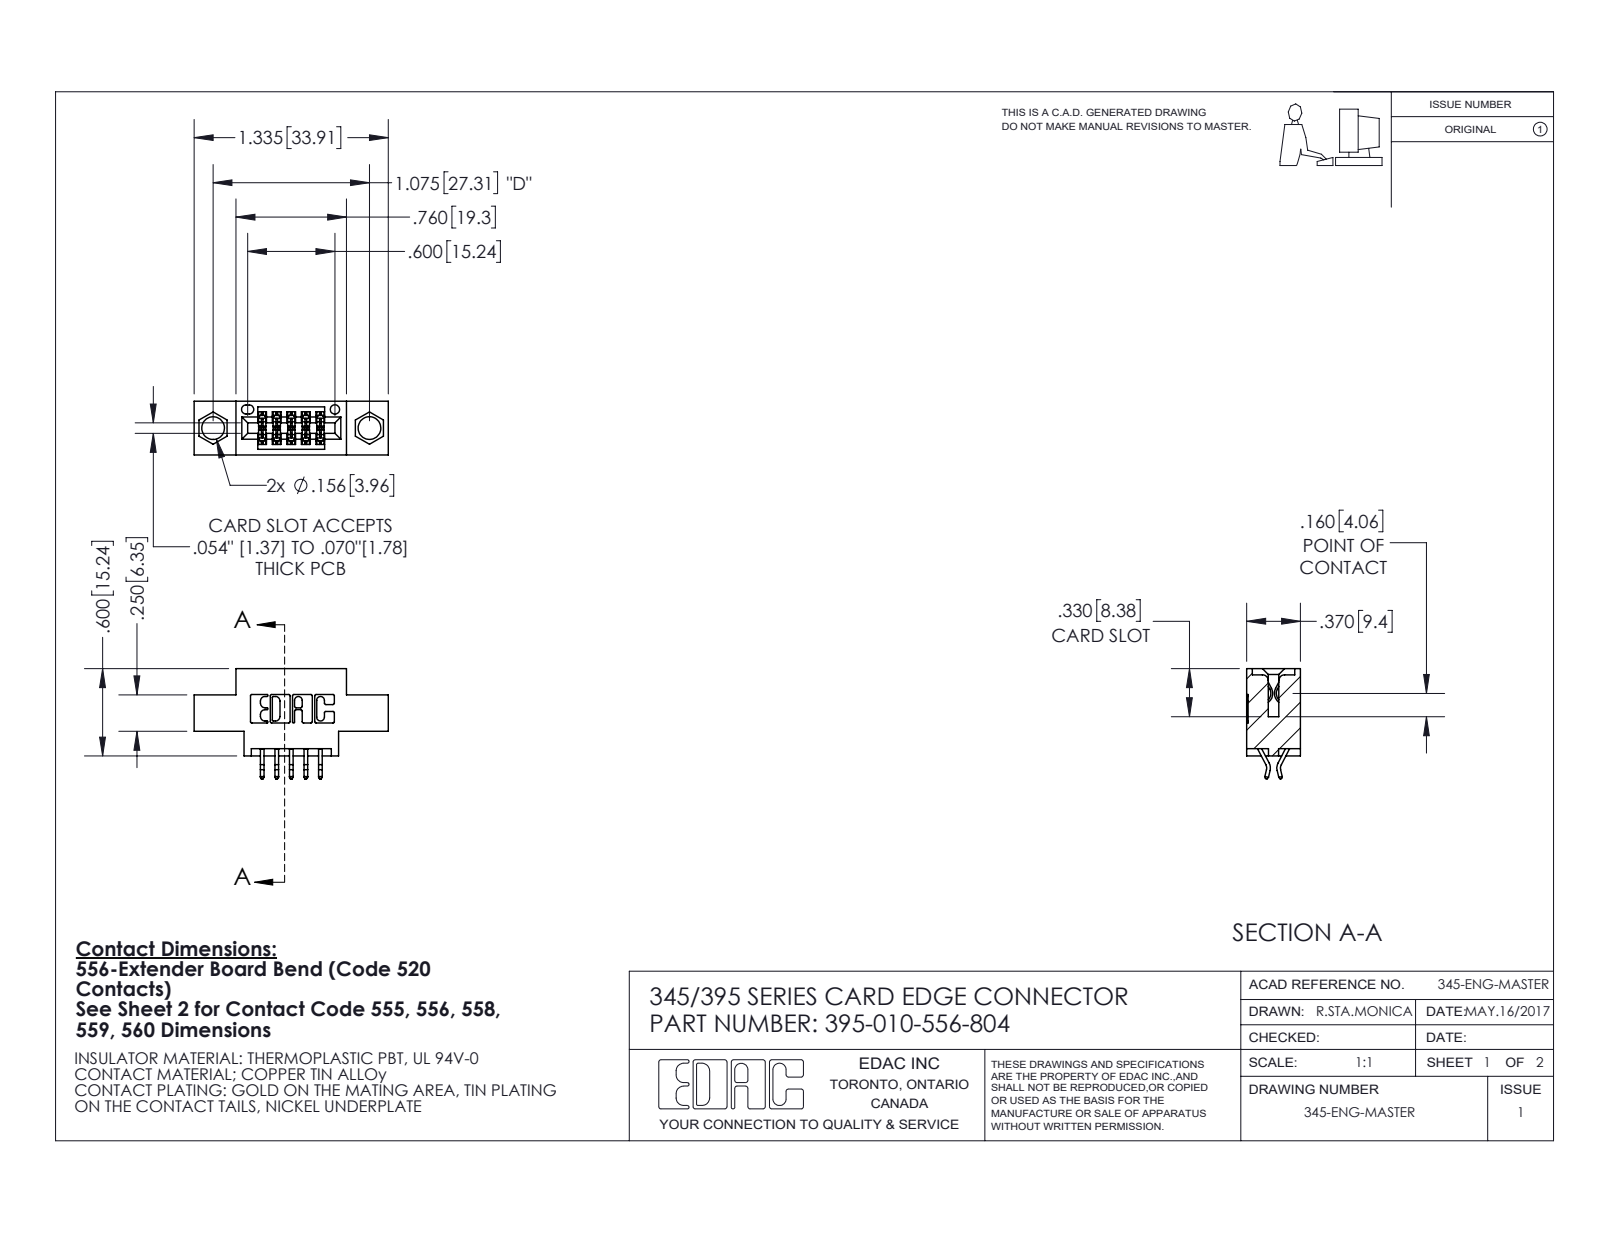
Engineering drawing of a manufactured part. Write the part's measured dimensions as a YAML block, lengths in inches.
part_name: "345 Part_0.170 Offset - 0.156 Dia-TI; 395-010-556-804; 345-292-001_556 Tail"
step_written_by: "SolidWorks 2020 (CONFIG_CONTROL_DESIGN)"
units: inches
bodies: {solids: 11, faces: 704, planar: 468, cylindrical: 236, other: 0}
overall_size: [1.335, 0.757, 0.37]
volume: 0.167
surface_area: 5.125
round_holes:
  - {diameter: 0.156, count: 2}
  - {diameter: 0.064, count: 1}
partial_cylinders:
  - {radius: 0.01, count: 22}
  - {radius: 0.006, count: 20}
  - {radius: 0.007, count: 6}
  - {radius: 0.031, count: 6}
  - {radius: 0.026, count: 3}
  - {radius: 0.01, count: 2}
  - {radius: 0.014, count: 2}
  - {radius: 0.019, count: 2}
face_to_face_distances: [0.37, 0.2, 0.072, 0.298, 0.1, 0.025, 0.25, 0.098, 0.272, 0.06]
hole_center_spacings: [0.27, 0.847, 1.075]
